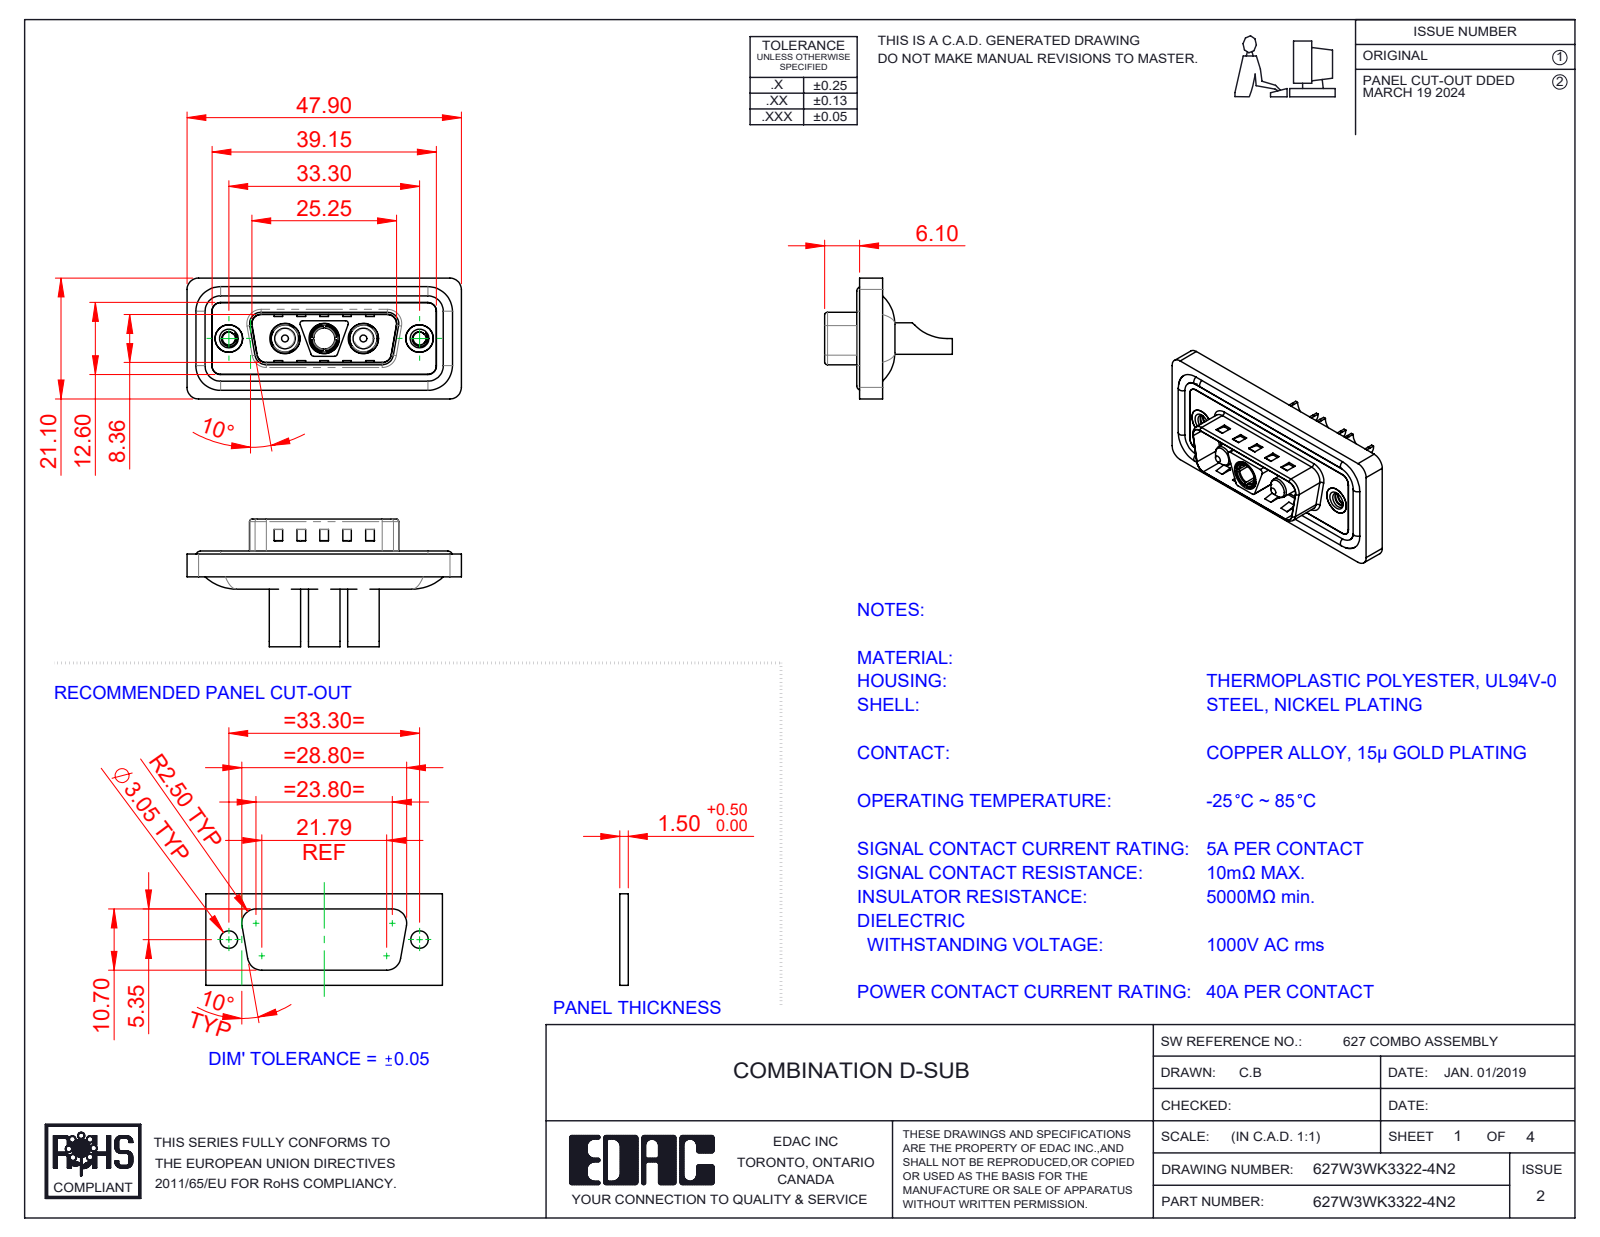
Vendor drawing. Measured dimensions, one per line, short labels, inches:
name: 627W3WK3322-4N2; 627Combo Waterproof Housing_15 Contacts; 627Combo Shell Front_15 Contacts; 627Combo Housing_3WK3 (+4 more)
written by: SolidWorks 2023 (CONFIG_CONTROL_DESIGN)
unit: in
bodies: 13 solids, 621 faces (237 planar, 253 cylindrical, 131 other)
size: 1.886 × 0.878 × 0.831
volume: 0.354 in³; area: 14.8 in²
holes: 3× ⌀0.181, 3× ⌀0.191, 3× ⌀0.209, 2× ⌀0.089, 2× ⌀0.157, 2× ⌀0.189, 2× ⌀0.197, 1× ⌀0.146
bosses: 4× ⌀0.063, 3× ⌀0.217, 3× ⌀0.205, 3× ⌀0.187, 3× ⌀0.148, 2× ⌀0.193, 2× ⌀0.142, 1× ⌀0.195
rounds: 26× R0.059, 20× R0.079, 12× R0.02, 8× R0.063, 4× R0.01, 4× R0.024, 4× R0.026, 4× R0.035
face distances: 0.016, 0.043, 0.02, 0.063, 0.122, 0.114, 0.059, 0.032, 0.377, 0.098
hole spacings: 0.27, 0.386, 0.656, 0.925, 0.539, 1.311
